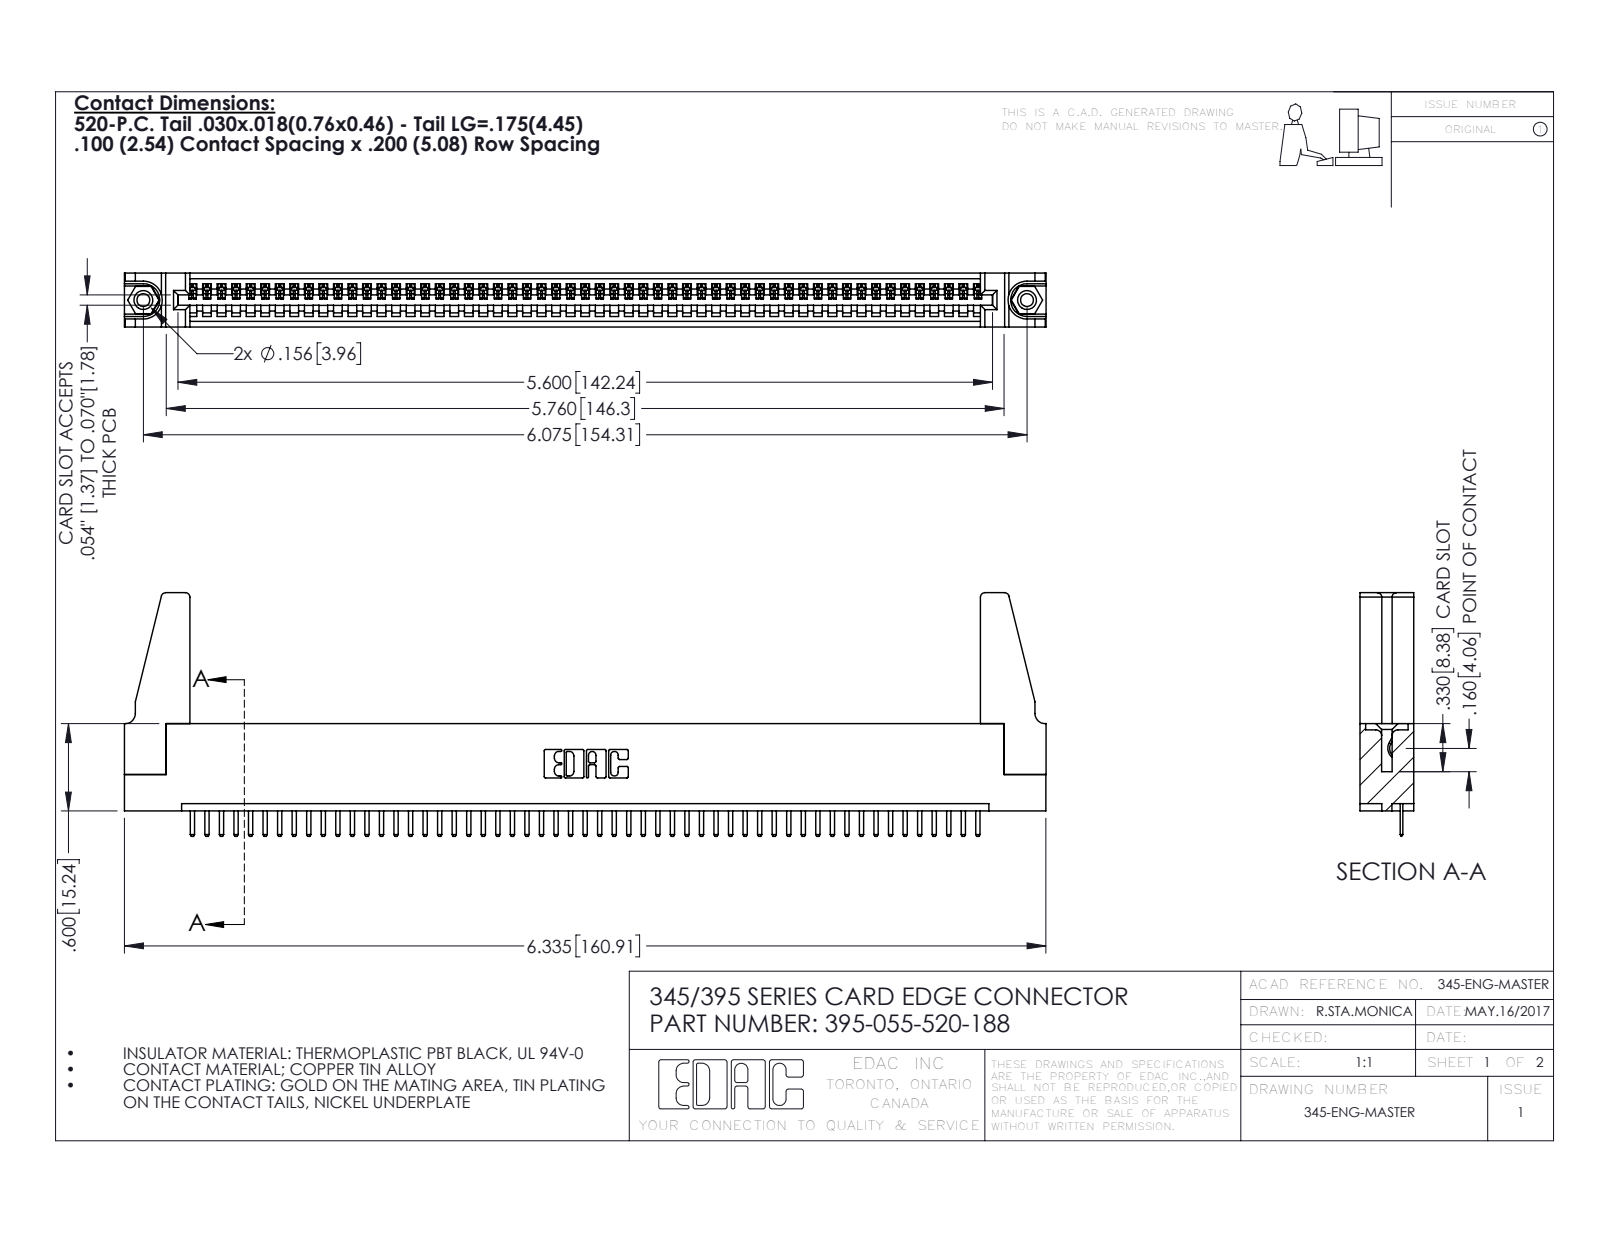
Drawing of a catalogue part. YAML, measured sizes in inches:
part_name: "395-055-520-188; 345-250-001_345-250-001-102; 345 Part_Flush Mounting Lugs - 0.156 Dia-TH; 345-292-001_345-293-120 (+1 more)"
step_written_by: "SolidWorks 2016 (CONFIG_CONTROL_DESIGN)"
units: inches
bodies: {solids: 60, faces: 3660, planar: 2462, cylindrical: 1182, other: 16}
overall_size: [6.336, 1.675, 0.37]
volume: 1.128
surface_area: 35.7
round_holes:
  - {diameter: 0.089, count: 2}
  - {diameter: 0.125, count: 2}
  - {diameter: 0.156, count: 2}
  - {diameter: 0.064, count: 1}
round_bosses_or_shafts:
  - {diameter: 0.155, count: 2}
partial_cylinders:
  - {radius: 0.01, count: 112}
  - {radius: 0.006, count: 110}
  - {radius: 0.01, count: 22}
  - {radius: 0.03, count: 8}
  - {radius: 0.007, count: 6}
  - {radius: 0.031, count: 6}
  - {radius: 0.026, count: 3}
  - {radius: 0.031, count: 2}
face_to_face_distances: [0.072, 0.298, 0.37, 0.2, 0.098, 0.272, 0.025, 0.225, 0.072, 0.149]
hole_center_spacings: [0.27, 5.839, 6.075]
